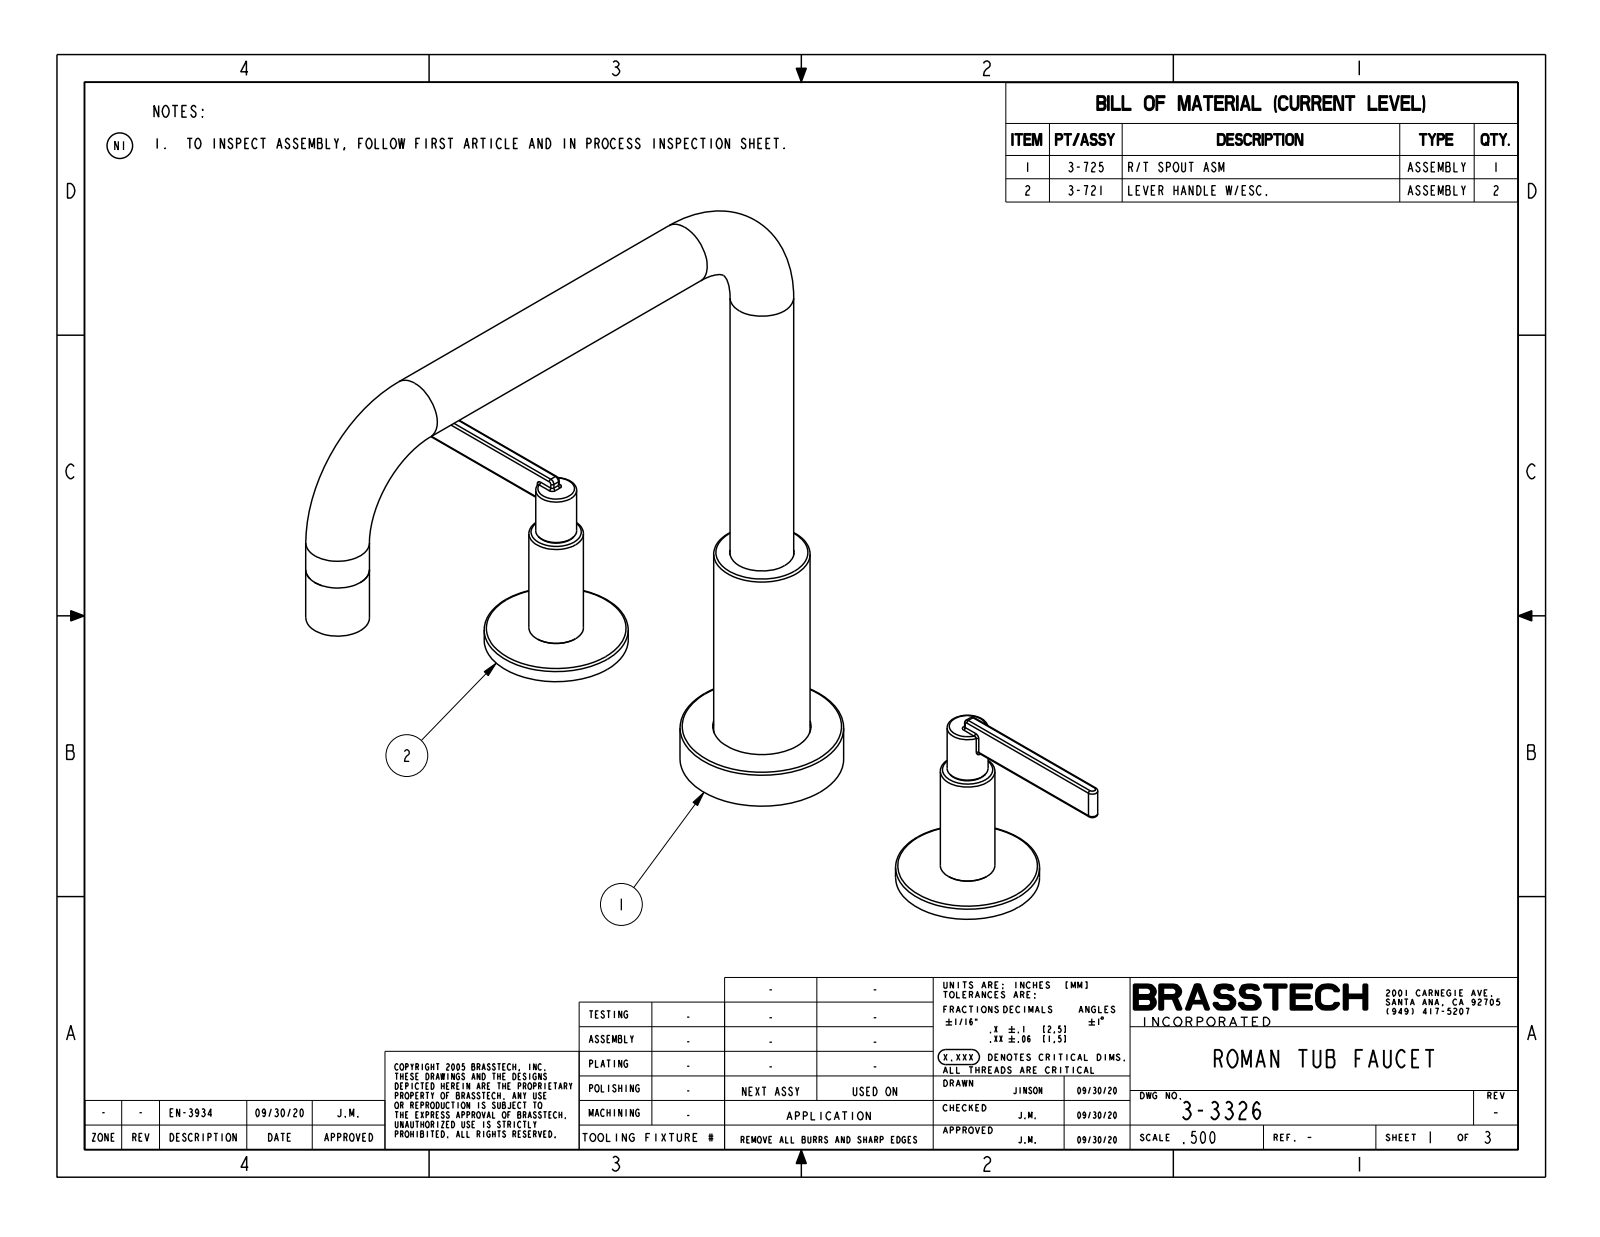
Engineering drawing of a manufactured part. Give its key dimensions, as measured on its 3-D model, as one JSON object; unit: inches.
{"part_name": "13539; 20-571_ASM; 13540; 13139 (+8 more)", "step_written_by": "CREO PARAMETRIC BY PTC INC, 2018400 (CONFIG_CONTROL_DESIGN)", "units": "inches", "bodies": {"solids": 11, "faces": 589, "planar": 184, "cylindrical": 275, "other": 130}, "overall_size": [13, 9.812, 9.748], "volume_in3": 8.331, "surface_area_in2": 165.7, "round_holes": [[0.751, 3], [0.11, 2], [0.36, 2], [0.397, 2], [0.4, 2], [0.516, 2], [0.535, 2], [0.6, 2], [0.7, 2], [1.6, 2], [1.89, 2], [0.118, 1]], "round_bosses_or_shafts": [[0.875, 3], [0.68, 3], [2, 2], [1.65, 2], [0.75, 2], [0.73, 2], [0.563, 2], [0.51, 2]], "partial_cylinders_radius": [[0.03, 16], [0.06, 2], [0.075, 2], [0.137, 2], [0.3, 1]], "face_to_face_distances": [0.05, 0.375, 0.15, 0.325, 0.15, 0.12, 0.07, 0.445, 0.08, 0.2], "hole_center_spacings": [4, 9.169, 8, 8.25]}
